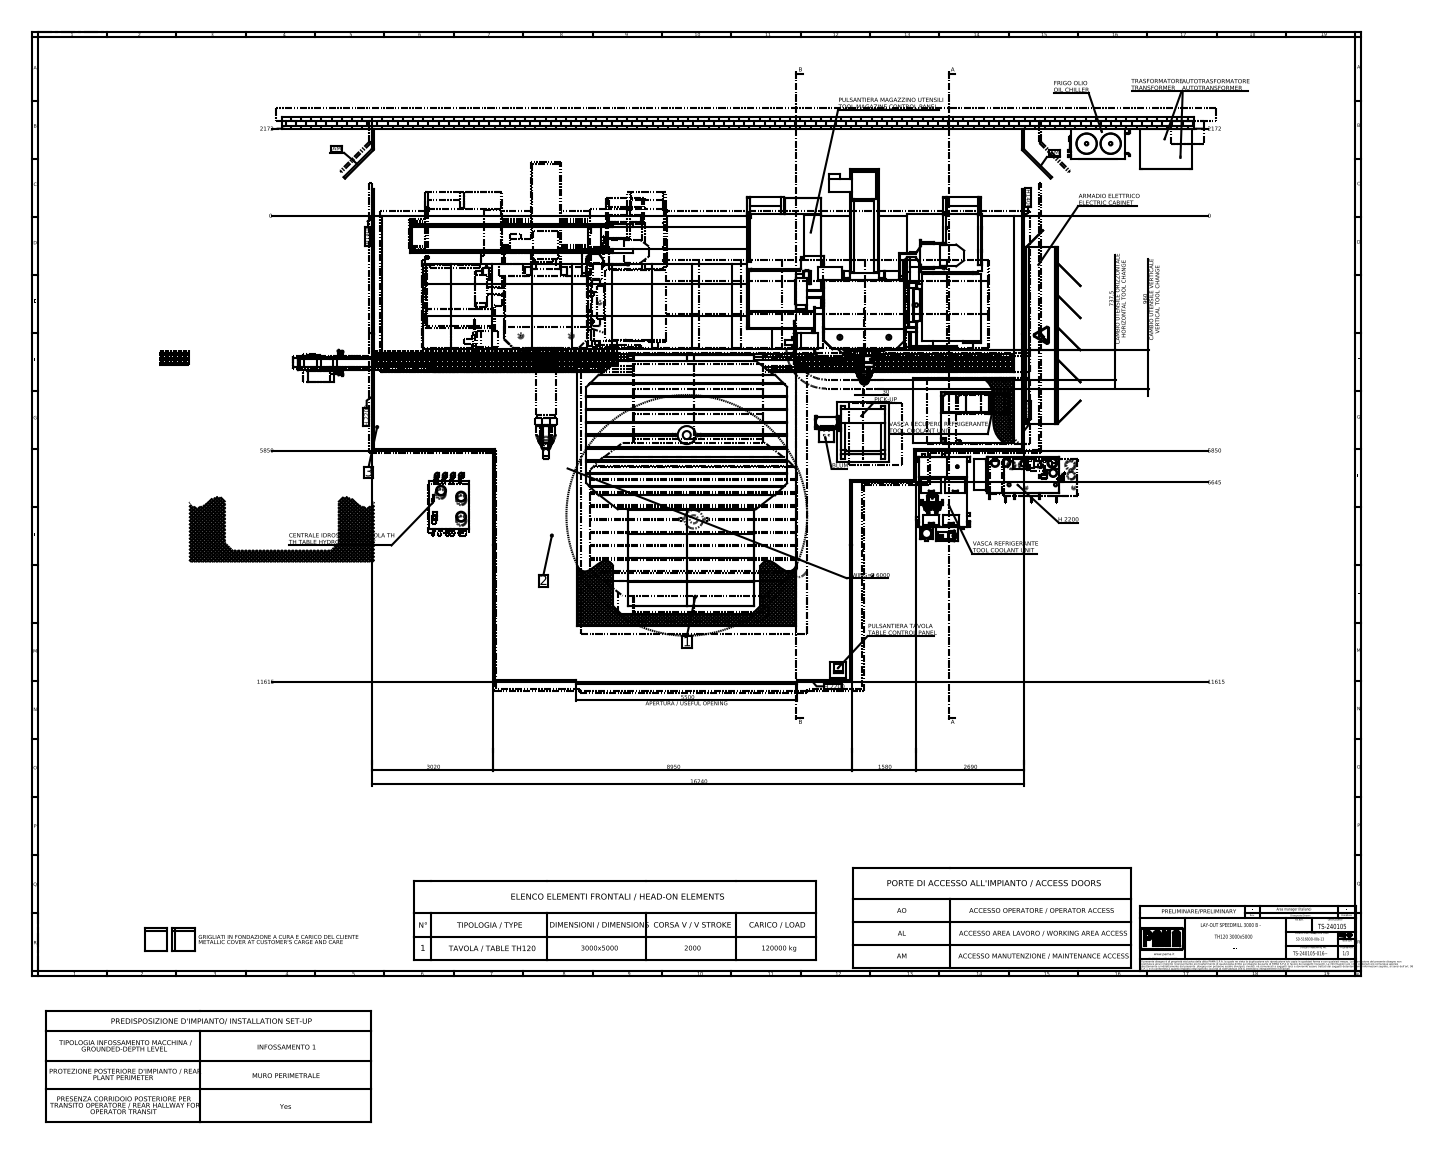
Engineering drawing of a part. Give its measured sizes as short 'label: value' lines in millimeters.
name: S002835_X=8000; S001576_DEFAULT<A macchina>; S002481_ANTE APERTE; S003390 (+8 more)
written by: SolidWorks 2023 (AUTOMOTIVE_DESIGN)
unit: mm
bodies: 561 solids, 8263 faces (6074 planar, 1762 cylindrical, 427 other)
size: 22740 × 17037 × 9400
volume: 798 400 000 000 mm³; area: 2 571 000 000 mm²
holes: 124× ⌀35, 63× ⌀69.6, 16× ⌀13, 8× ⌀14, 6× ⌀8, 6× ⌀32, 5× ⌀12, 4× ⌀6.8, 4× ⌀7, 4× ⌀12.5, 3× ⌀50, 3× ⌀56.66
bosses: 14× ⌀20, 12× ⌀60, 10× ⌀9, 9× ⌀80, 8× ⌀200, 8× ⌀55, 8× ⌀30, 7× ⌀66.3
rounds: 237× R5, 73× R10, 46× R15, 37× R6, 29× R2, 26× R35, 18× R20, 16× R8
face distances: 2000, 300, 50, 450, 1550, 17037, 16737, 22740, 1026, 524
hole spacings: 250, 500, 750, 1000, 1250, 1500, 1750, 2000
